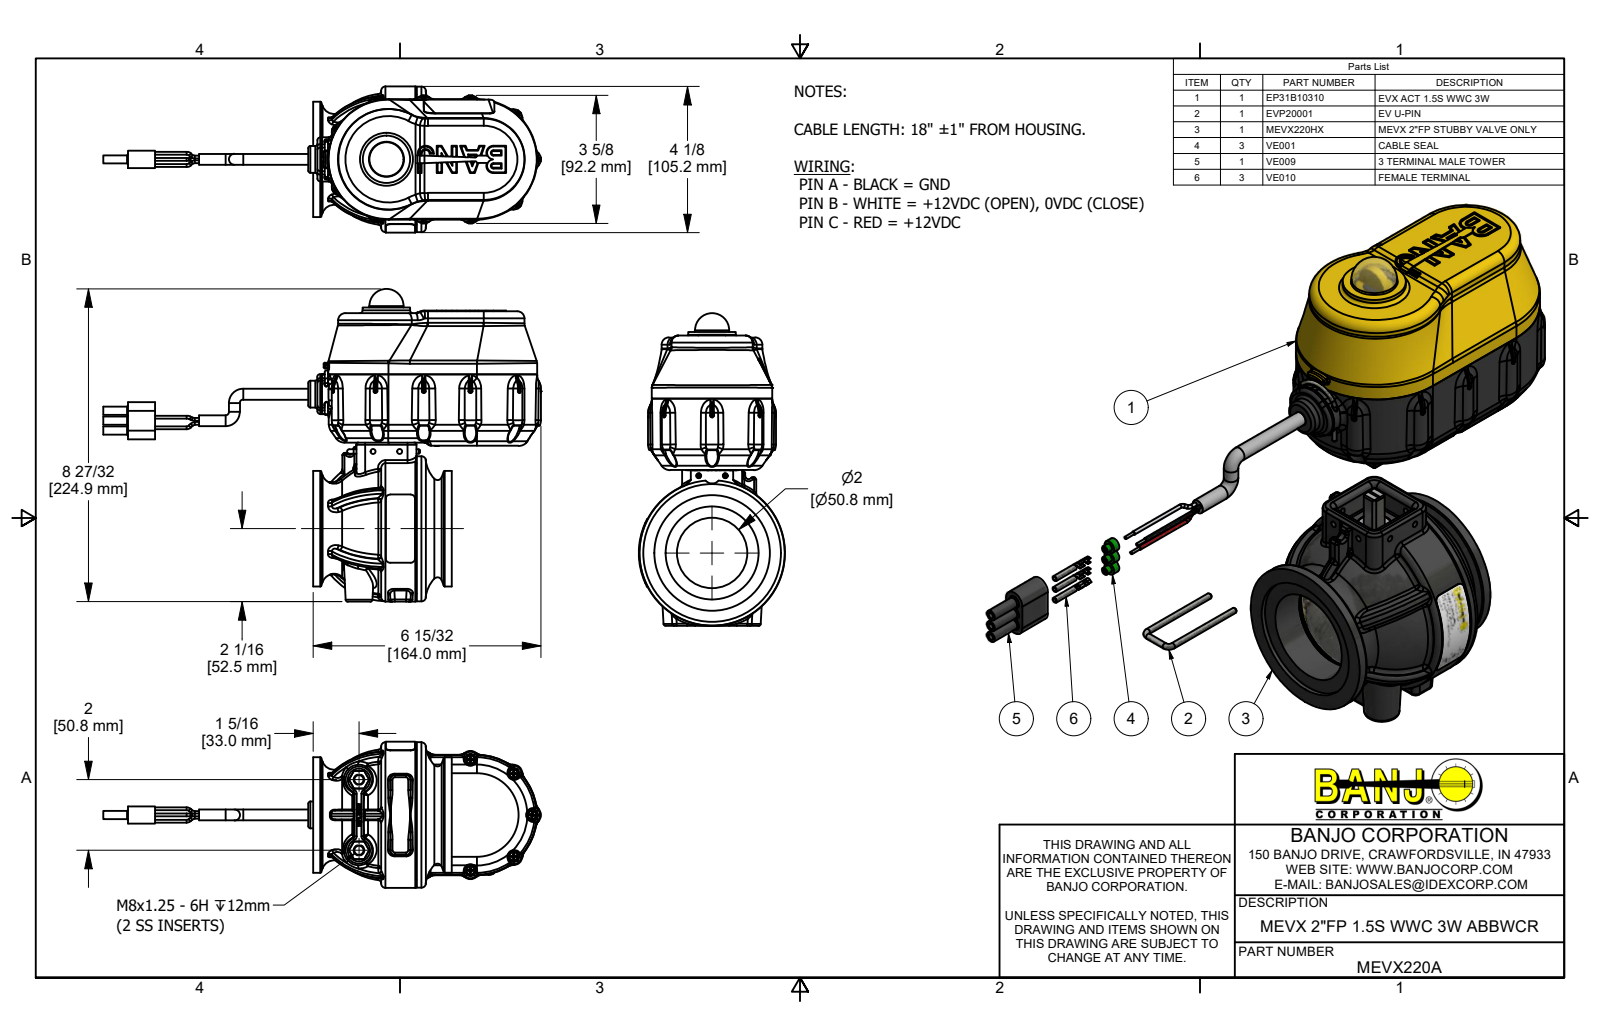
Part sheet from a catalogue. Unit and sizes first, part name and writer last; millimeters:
Units: millimetres
Overall size (bounding box): 315 × 224.9 × 105.2
Round holes (diameter × count): ⌀2.4 ×11, ⌀3.8 ×11, ⌀2 ×7, ⌀3.4 ×5, ⌀2.7 ×4, ⌀3.2 ×4, ⌀3.5 ×4, ⌀3.8 ×4, ⌀3.8 ×4, ⌀4.3 ×4, ⌀1.2 ×3, ⌀2.4 ×3
Round bosses / shafts (diameter × count): ⌀6.4 ×17, ⌀2 ×15, ⌀3.6 ×11, ⌀2.7 ×11, ⌀2.2 ×11, ⌀1.5 ×6, ⌀6.9 ×4, ⌀5.6 ×4
Partial cylindrical surfaces — rounded edges, fillets, slot ends (radius × count): R0.3 ×180, R1 ×145, R0.3 ×84, R0.5 ×71, R0.1 ×55, R0.8 ×34, R1.5 ×31, R2 ×28
Main face-to-face distances: 2.5, 65.2, 1.5, 5.4, 3.8, 48.2, 46.6, 42.8, 14.5, 16
Hole centre spacings: 56.4, 32.6, 68.3, 69, 19.1, 24, 42.2, 45.1
Volume: 876 400 mm³ · Surface area: 397 700 mm²
Bodies: 91 solids, 10907 faces (2890 planar, 3113 cylindrical, 4904 other)
Part name (STEP PRODUCT): MEVX220A; EP31B10310; B61905PPHS; B632038PM (+8 more)
STEP written by: Autodesk Inventor 2019 (AUTOMOTIVE_DESIGN)
